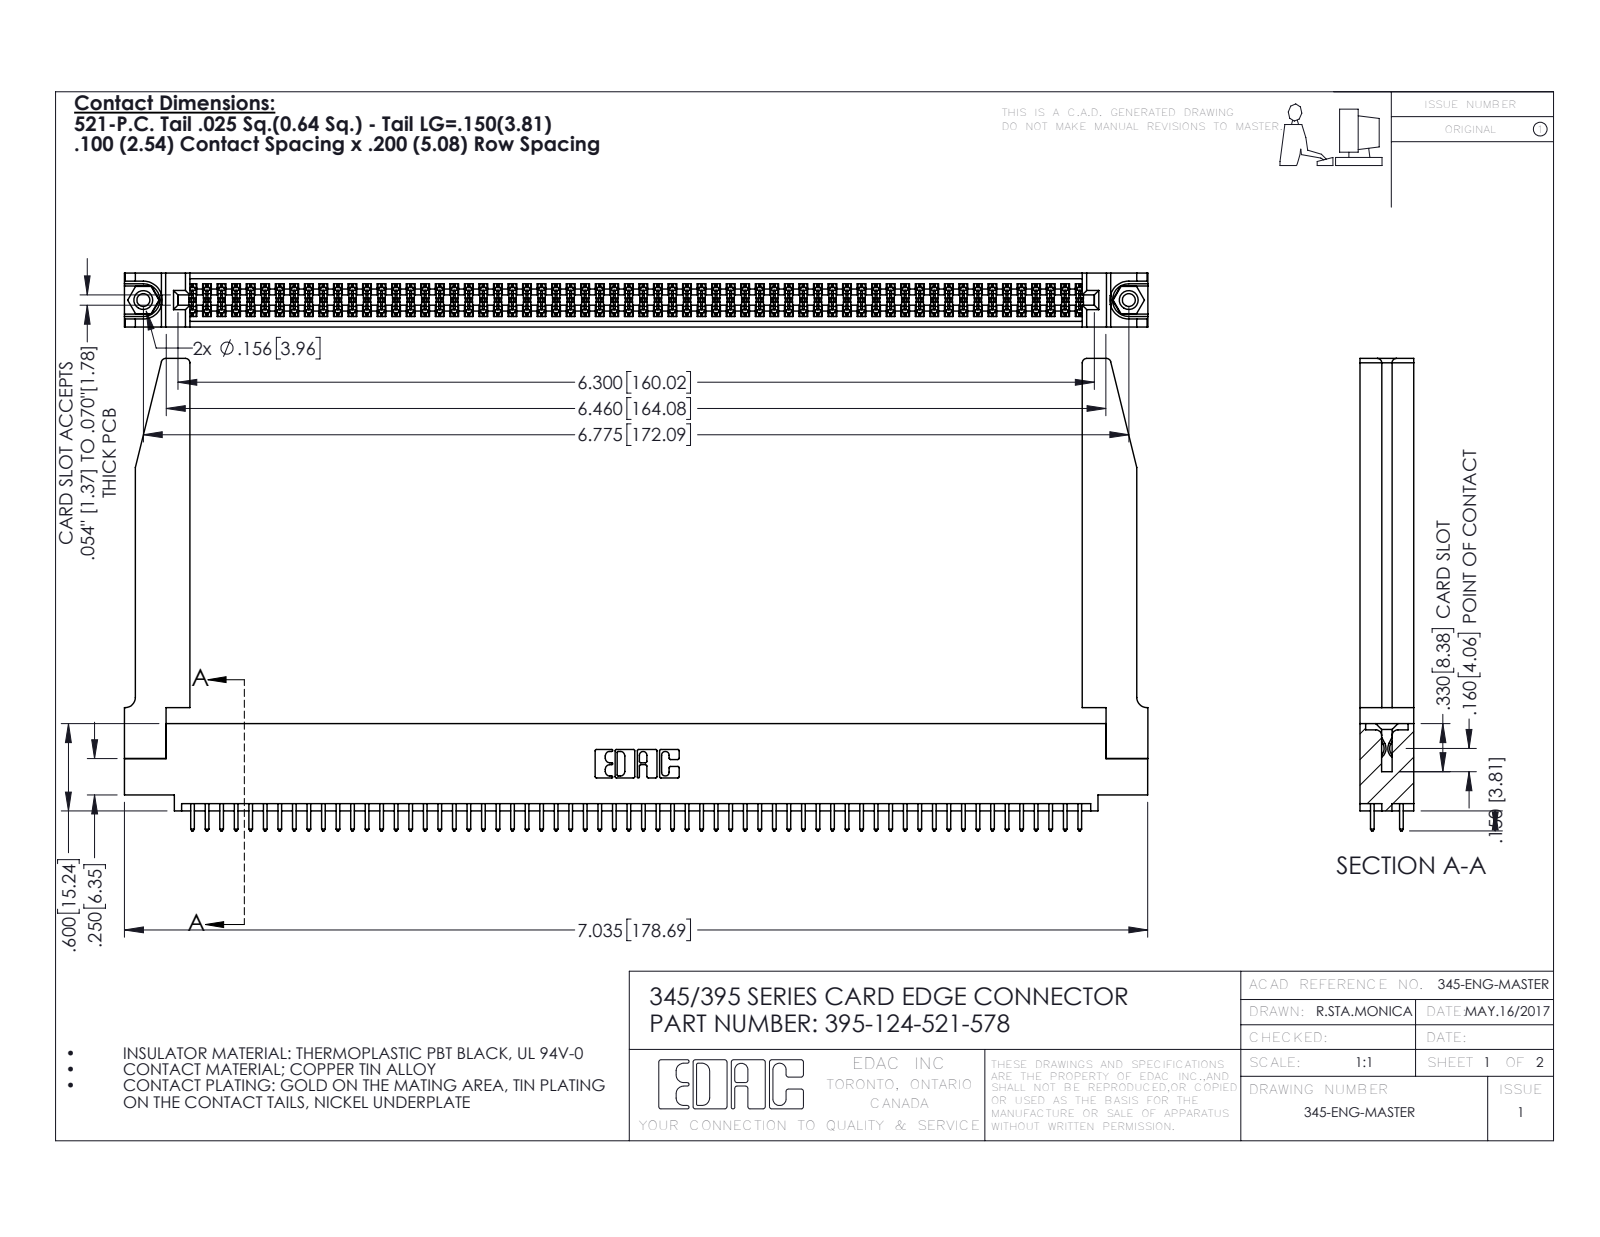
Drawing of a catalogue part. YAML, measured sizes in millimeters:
part_name: "345 Part_0.110 Offset - 0.156 Dia-TH; 345-292-001_345-293-121; 345-250-001_345-250-001-102; 345-220-078_345-220-078 (+1 more)"
step_written_by: "SolidWorks 2016 (CONFIG_CONTROL_DESIGN)"
units: millimeters
bodies: {solids: 129, faces: 6564, planar: 4318, cylindrical: 2194, other: 52}
overall_size: [178.7, 82.5, 9.4]
volume: 25190
surface_area: 32740
round_holes:
  - {diameter: 2.3, count: 2}
  - {diameter: 3.2, count: 2}
  - {diameter: 4, count: 2}
  - {diameter: 1.6, count: 1}
round_bosses_or_shafts:
  - {diameter: 3.9, count: 2}
partial_cylinders:
  - {radius: 0.2, count: 186}
  - {radius: 0.3, count: 124}
  - {radius: 0.3, count: 22}
  - {radius: 0.8, count: 8}
  - {radius: 0.2, count: 6}
  - {radius: 0.8, count: 6}
  - {radius: 0.7, count: 3}
  - {radius: 0.4, count: 2}
face_to_face_distances: [1.8, 7.6, 9.4, 2.5, 6.9, 0.6, 5.1, 5.7, 4.4, 3.8]
hole_center_spacings: [6.9, 166.1, 172.1]
